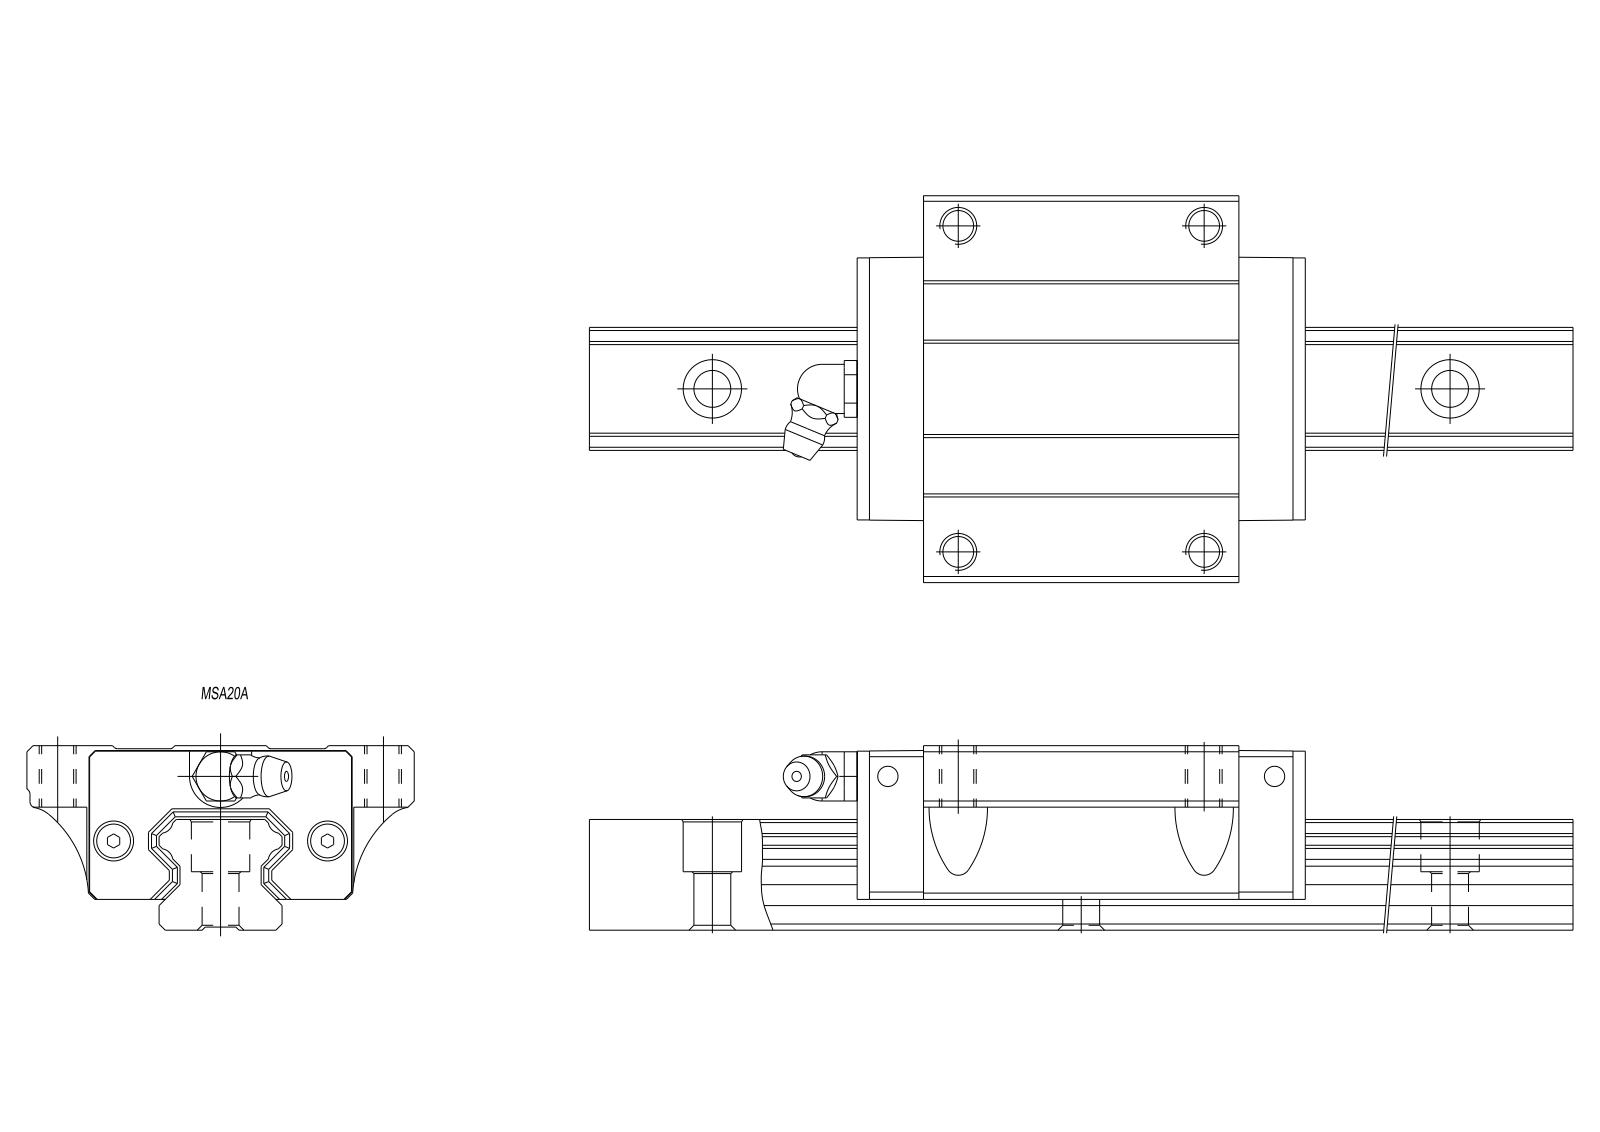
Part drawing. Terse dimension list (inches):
written by: Kubotek KeyCreator V6.5.2 (0407) (CONFIG_CONTROL_DESIGN)
unit: in
bodies: 3 solids, 223 faces (142 planar, 64 cylindrical, 17 other)
size: 8.661 × 2.48 × 1.181
volume: 8.269 in³; area: 56.95 in²
holes: 8× ⌀0.236, 4× ⌀0.374, 2× ⌀0.128, 2× ⌀0.256
bosses: 1× ⌀0.315
rounds: 4× R0.087, 4× R0.187, 2× R0.039, 2× R0.197, 2× R0.709, 1× R0.199
face distances: 0.709, 0.02, 0.472, 1.181, 1.161, 0.197, 0.512, 0.984, 0.137, 0.651
hole spacings: 1.115, 2.228, 2.947, 4.455, 2.362, 1.575, 2.087, 2.614
